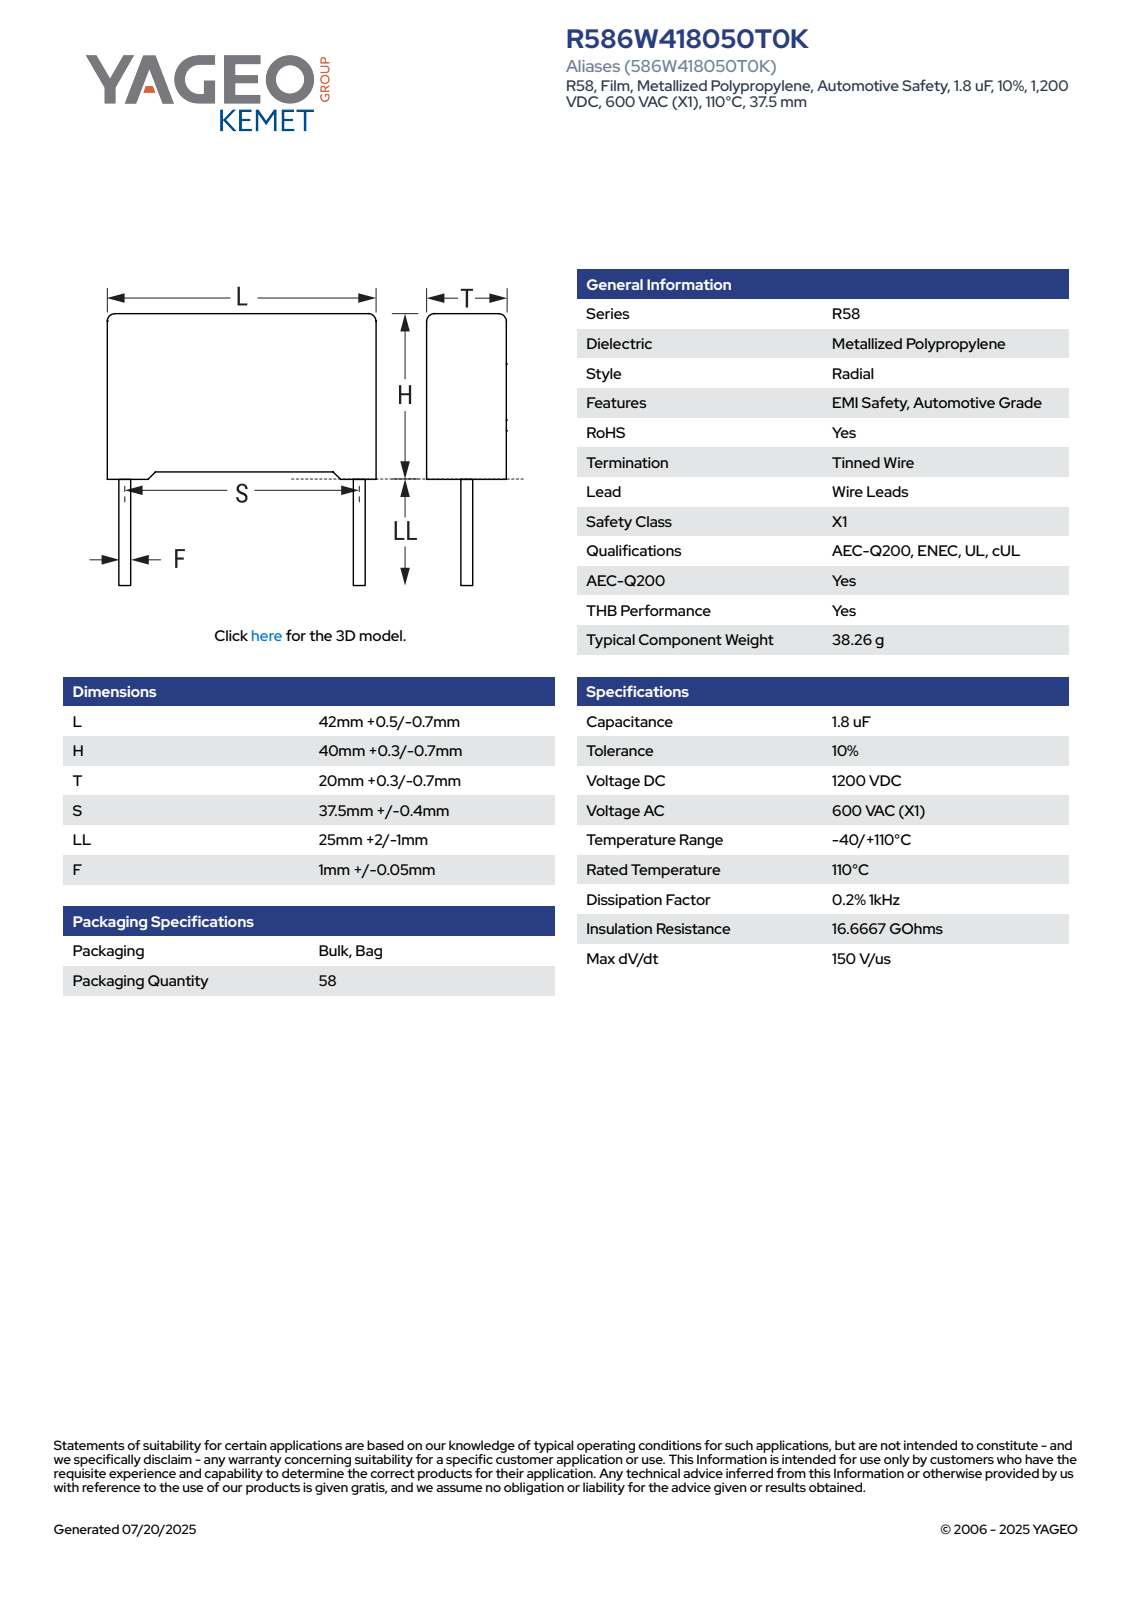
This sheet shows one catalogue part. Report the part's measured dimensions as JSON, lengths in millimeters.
{"part_name": "CFR_RB2_42X40X20_L42.5H40.3T20.3S37.5LL27F1.05", "step_written_by": "SolidWorks 2021 (AUTOMOTIVE_DESIGN)", "units": "millimeters", "bodies": {"solids": 4, "faces": 85, "planar": 77, "cylindrical": 8, "other": 0}, "overall_size": [67.3, 42.5, 20.3], "volume_mm3": 33795, "surface_area_mm2": 7035, "round_bosses_or_shafts": [[1.05, 2]], "partial_cylinders_radius": [[0.5, 4]], "face_to_face_distances": [20.3, 42.5, 38.91, 0.64, 39.55, 0.75, 1.39, 40.3, 1.42, 20.31]}
